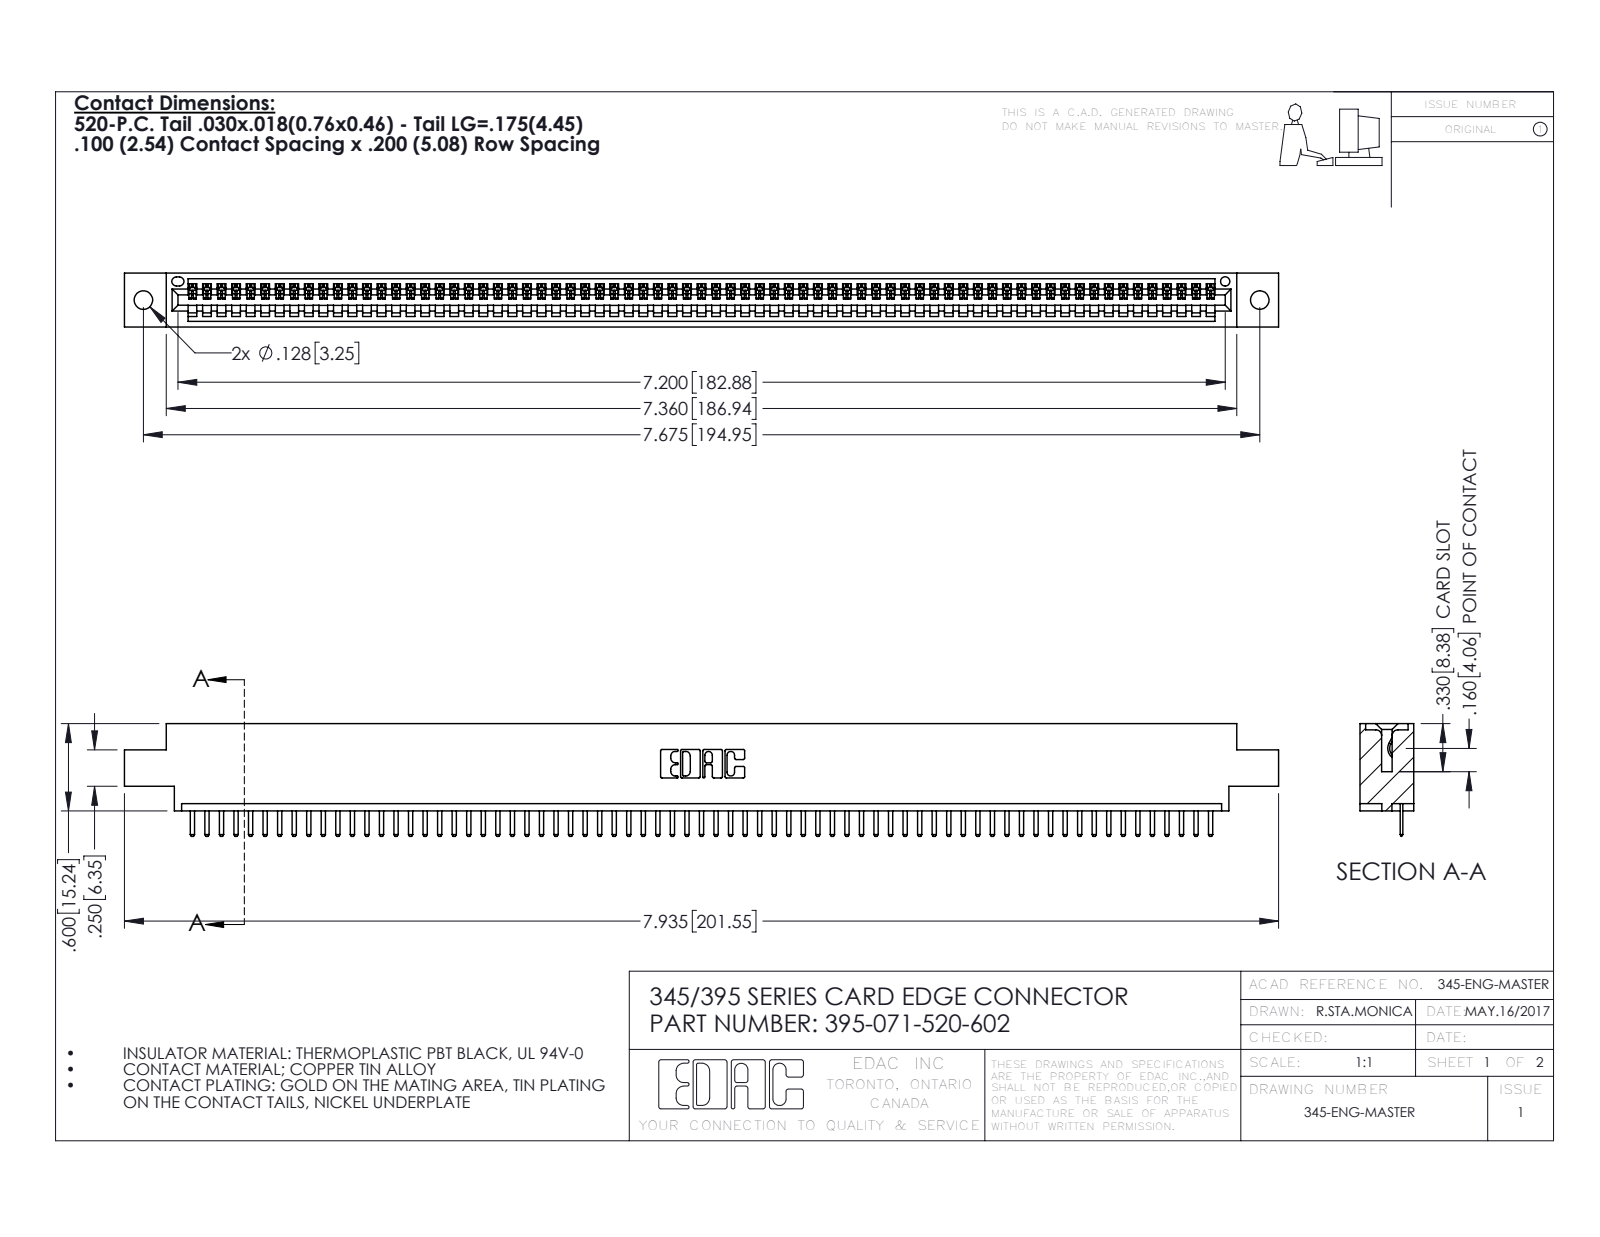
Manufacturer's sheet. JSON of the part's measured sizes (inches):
{"part_name": "345 Part_0.170 Offset - 0.128 Dia; 395-071-520-602; 345-292-001_345-293-120", "step_written_by": "SolidWorks 2016 (CONFIG_CONTROL_DESIGN)", "units": "inches", "bodies": {"solids": 72, "faces": 4532, "planar": 3066, "cylindrical": 1466, "other": 0}, "overall_size": [7.935, 0.775, 0.37], "volume_in3": 1.161, "surface_area_in2": 38.54, "round_holes": [[0.128, 2], [0.064, 1]], "partial_cylinders_radius": [[0.01, 144], [0.006, 142], [0.01, 22], [0.007, 6], [0.031, 6], [0.026, 3], [0.031, 2], [0.04, 2]], "face_to_face_distances": [0.298, 0.072, 0.37, 0.2, 0.098, 0.272, 0.025, 0.225, 0.072, 0.175], "hole_center_spacings": [0.27, 7.439, 7.675]}
